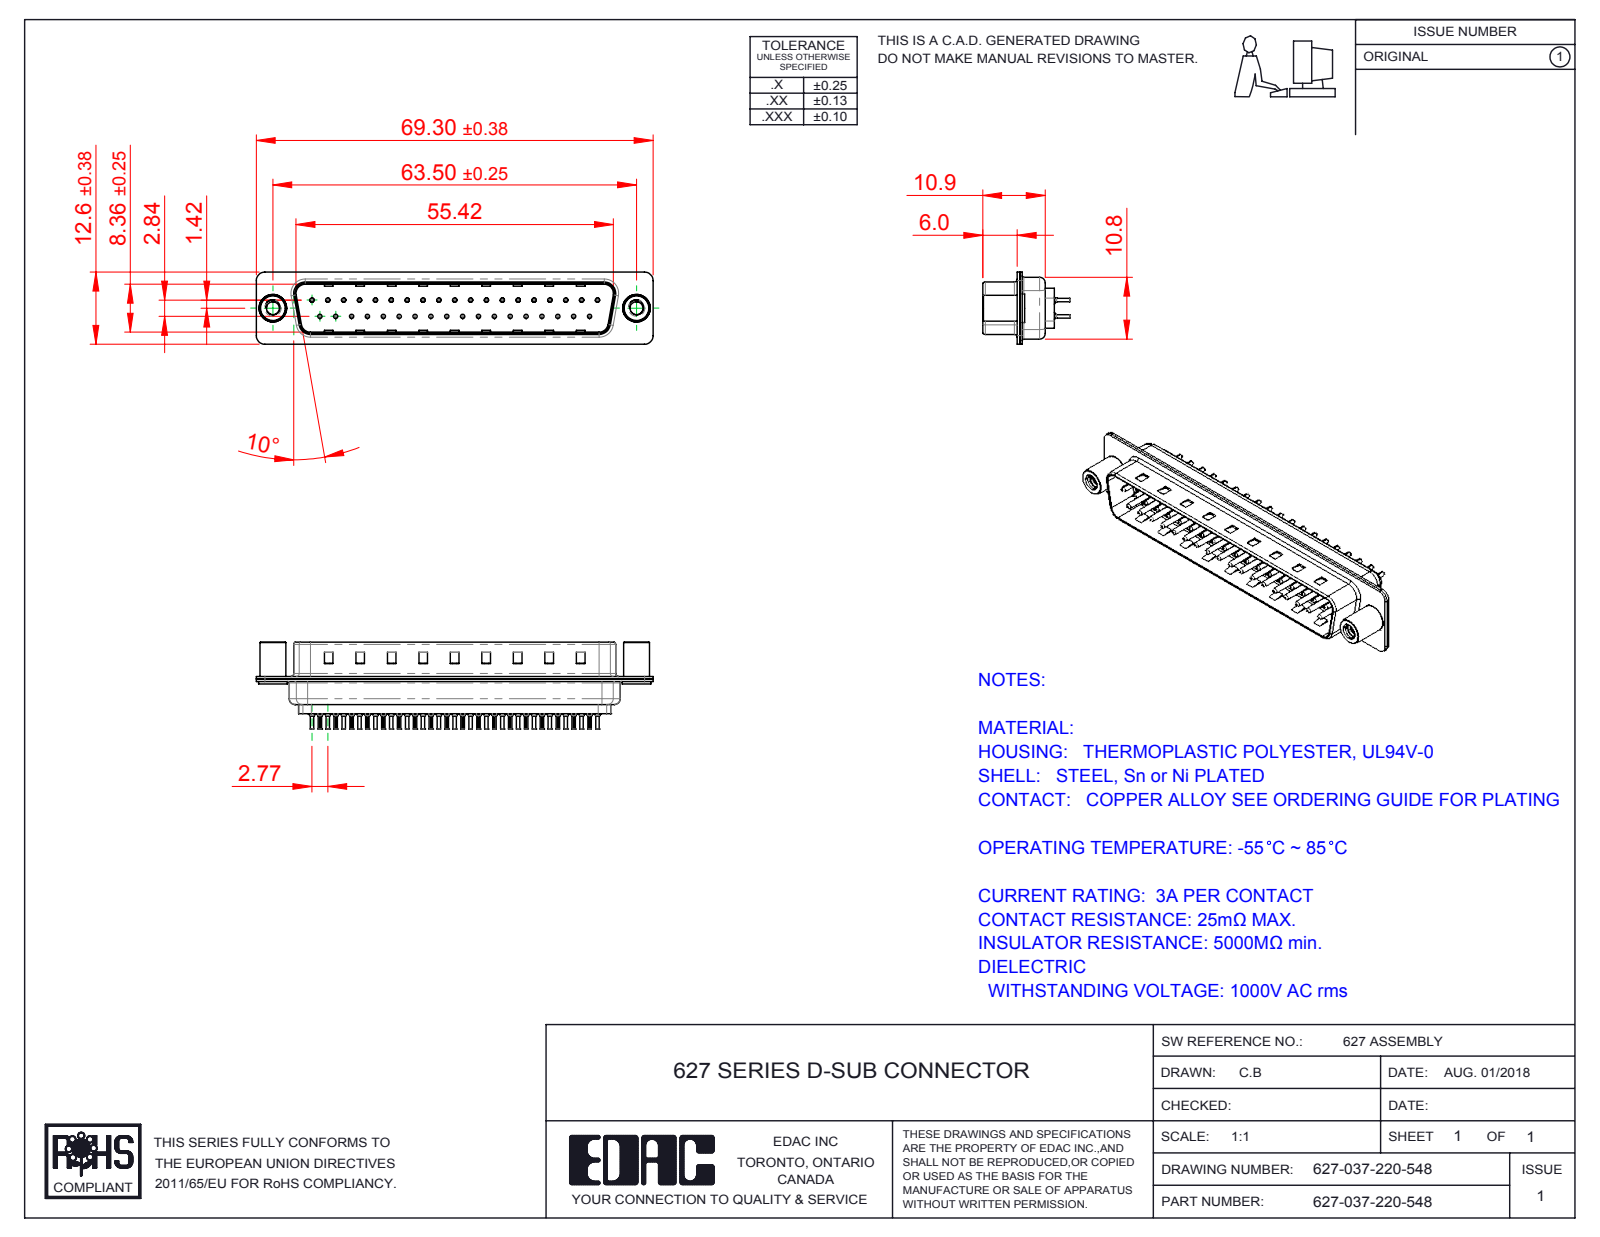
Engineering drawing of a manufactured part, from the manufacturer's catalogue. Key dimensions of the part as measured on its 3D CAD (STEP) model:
Part name (STEP PRODUCT): 627 4-40 Threaded Standoff; 627 Shell Rear_37 Contacts; 627 Shell Front_37 Contacts; 627 Contact Row 1_20L (+3 more)
STEP written by: SolidWorks 2016 (CONFIG_CONTROL_DESIGN)
Units: millimetres
Bodies: 42 solids, 4072 faces (1093 planar, 1538 cylindrical, 1441 other)
Overall size (bounding box): 69.3 × 15.2 × 12.6
Volume: 3 746 mm³ · Surface area: 10 657 mm²
Round holes (diameter × count): ⌀0.2 ×37, ⌀0.35 ×37, ⌀1.1 ×37, ⌀1.6 ×37, ⌀2.26 ×2, ⌀4 ×2, ⌀4.8 ×2
Round bosses / shafts (diameter × count): ⌀2 ×37, ⌀1.5 ×37, ⌀0.75 ×37, ⌀0.6 ×37, ⌀5 ×2, ⌀4.9 ×2, ⌀4.5 ×2
Partial cylindrical surfaces — rounded edges, fillets, slot ends (radius × count): R0.1 ×74, R1.5 ×16, R2 ×12, R0.5 ×8, R1.6 ×8, R0.25 ×4, R0.6 ×4, R0.65 ×4
Main face-to-face distances: 0.4, 0.82, 9.58, 0.45, 8.76, 1.5, 0.9, 1.4, 6.05, 0.42
Hole centre spacings: 3.16, 2.77, 5.54, 8.31, 5.04, 10.1, 11.08, 12.78
